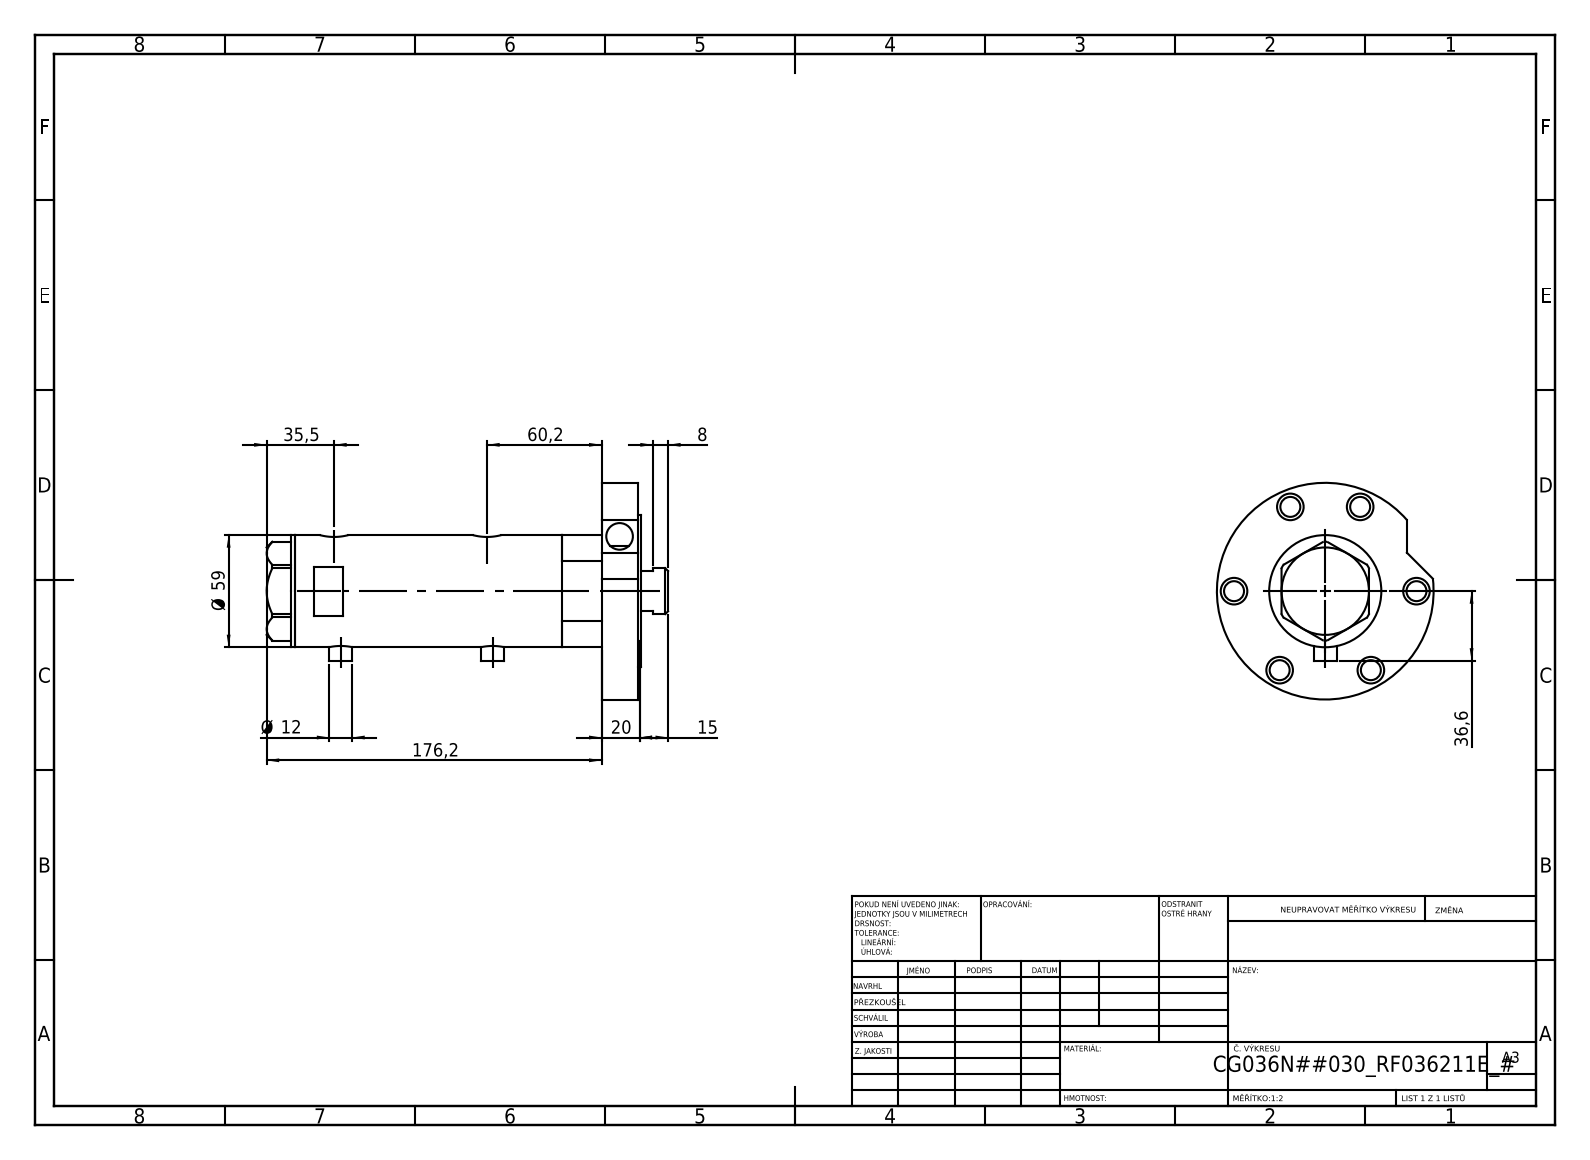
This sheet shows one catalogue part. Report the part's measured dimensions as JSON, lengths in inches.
{"part_name": "V270CG_FRONT; V270CG_VC; V270CG_MIDDLE; V270CG_RF211E (+1 more)", "step_written_by": "SolidWorks 2019 (CONFIG_CONTROL_DESIGN)", "units": "inches", "bodies": {"solids": 5, "faces": 164, "planar": 62, "cylindrical": 82, "other": 20}, "overall_size": [8.315, 4.488, 4.488], "volume_in3": 38.15, "surface_area_in2": 207.9, "round_holes": [[0.551, 7], [0.413, 6], [0.383, 2], [0.492, 2], [0.591, 2], [0.335, 1], [0.984, 1], [1.043, 1], [1.417, 1], [1.575, 1], [1.89, 1], [2.047, 1]], "round_bosses_or_shafts": [[0.472, 2], [4.488, 1], [3.15, 1], [2.323, 1], [1.811, 1], [0.945, 1]], "face_to_face_distances": [0.079, 0.748, 0.827, 7.173, 6.346, 7.094, 4.024, 2.323, 3.071, 3.15], "hole_center_spacings": [1.89, 2.1, 3.143, 3.273, 3.39, 3.772, 0.114, 0.138]}
